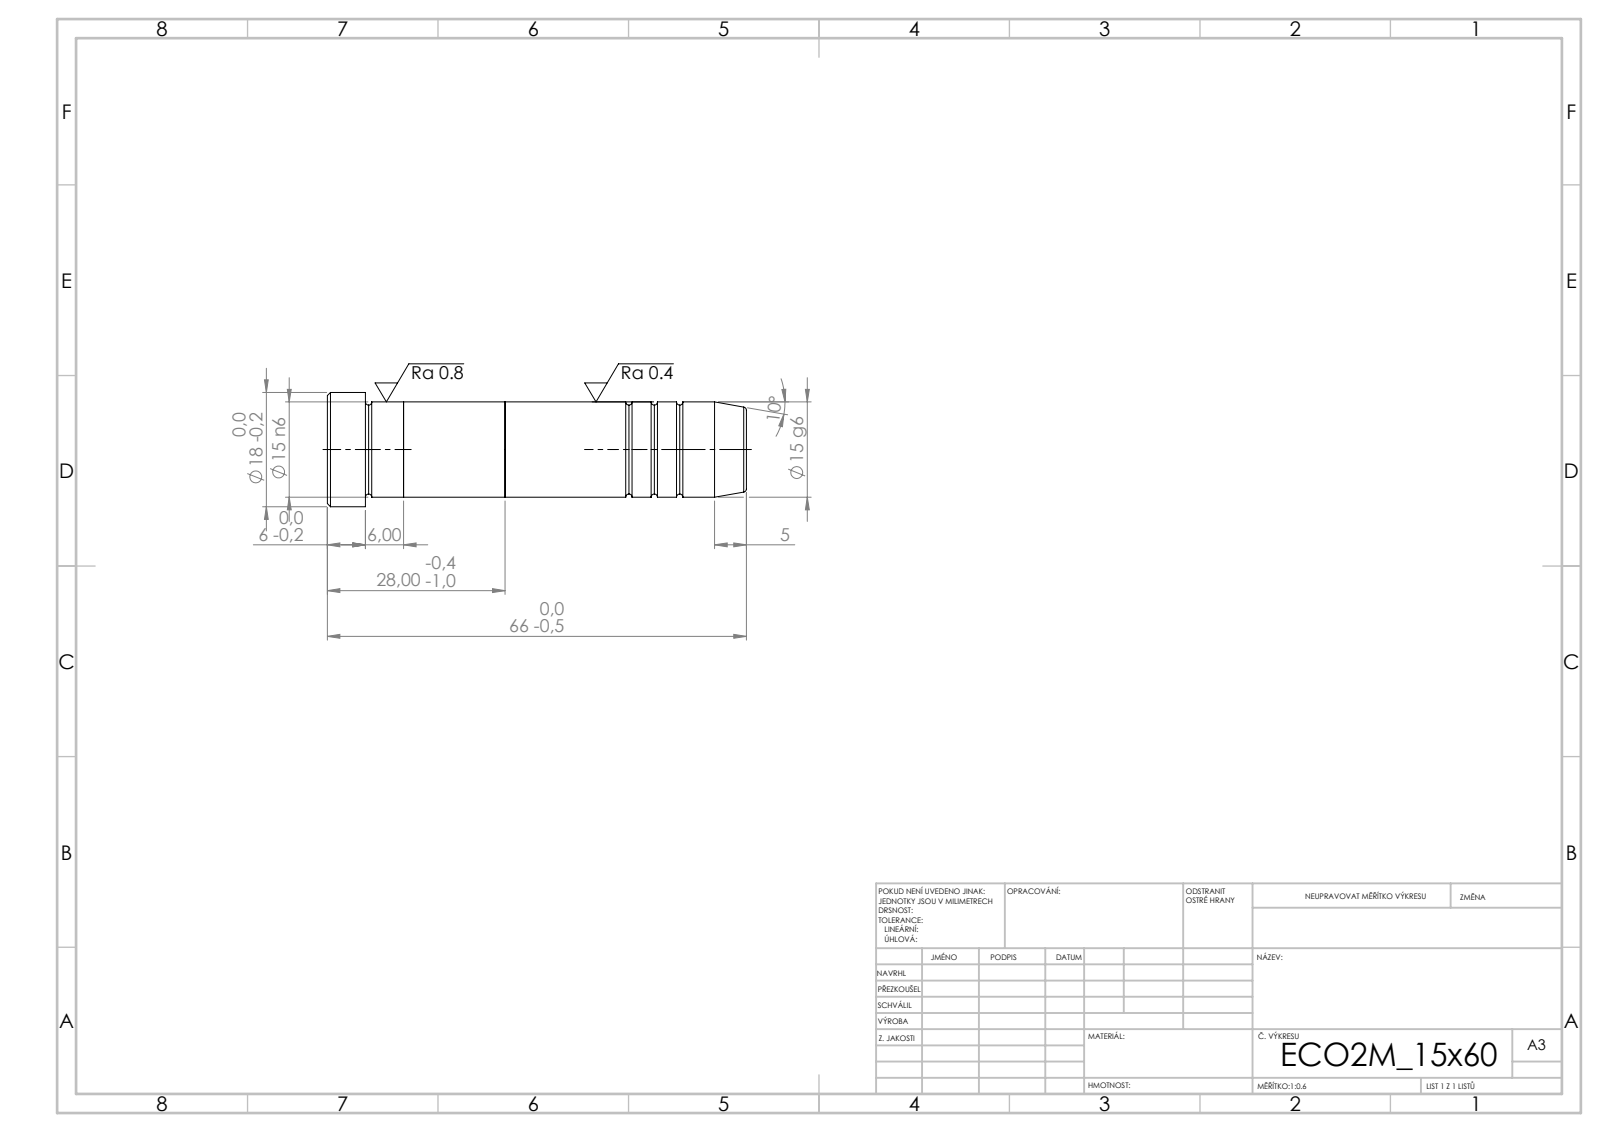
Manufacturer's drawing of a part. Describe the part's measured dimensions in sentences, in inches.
Its 3-D file was written by "SolidWorks 2019 (CONFIG_CONTROL_DESIGN)". It is 3 solids with 43 faces: 7 planar, 14 cylindrical and 22 other. Overall it measures 2.598 by 0.709 by 0.709 inches. Its volume is 0.729 cubic inches and its surface area 6.828 square inches. Round bosses or shafts: 1 of diameter 0.709, 1 of diameter 0.591. The main face-to-face distances are 0.63, 1.102, 0.472, 0.236, 1.496, 2.126, 2.598, 2.362, 0.866.
